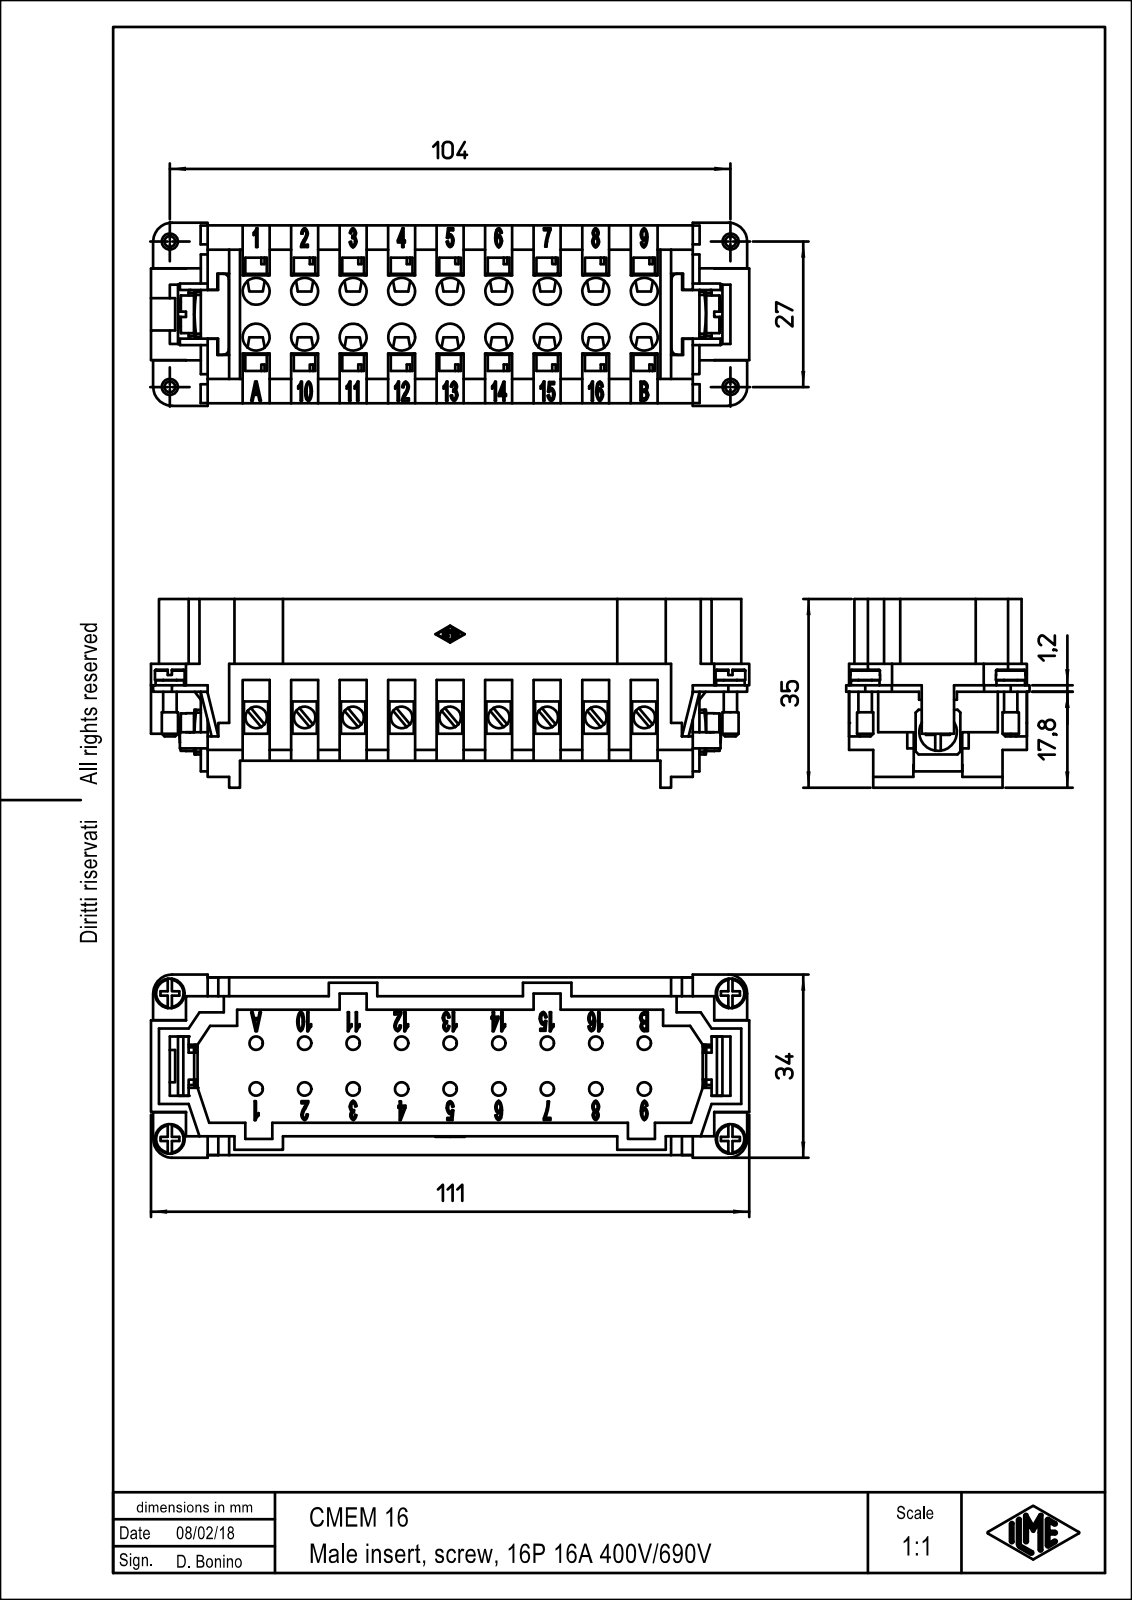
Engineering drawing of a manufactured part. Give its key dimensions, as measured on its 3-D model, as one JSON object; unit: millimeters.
{"part_name": "CMEM_16", "step_written_by": "PTC Creo Elements/Direct Modeling 19.0B 21-Mar-2015 (C) Parametric Technology GmbH (AUTOMOTIVE_DESIGN)", "units": "millimeters", "bodies": {"solids": 1, "faces": 1717, "planar": 1133, "cylindrical": 192, "other": 392}, "overall_size": [111, 35, 34], "volume_mm3": 50212, "surface_area_mm2": 30534, "round_holes": [[5, 18], [2.55, 4]], "round_bosses_or_shafts": [[2.5, 22], [4, 11], [5.5, 4], [5.3, 4], [3, 4], [7, 1]], "partial_cylinders_radius": [[0.1, 14], [1, 4], [3.5, 4], [2, 2], [5.5, 1]], "face_to_face_distances": [27, 18, 9, 5, 13, 2.5, 14, 4, 36, 23], "hole_center_spacings": [9, 12.38, 18, 19.91, 27, 28.31, 36, 36.99]}
